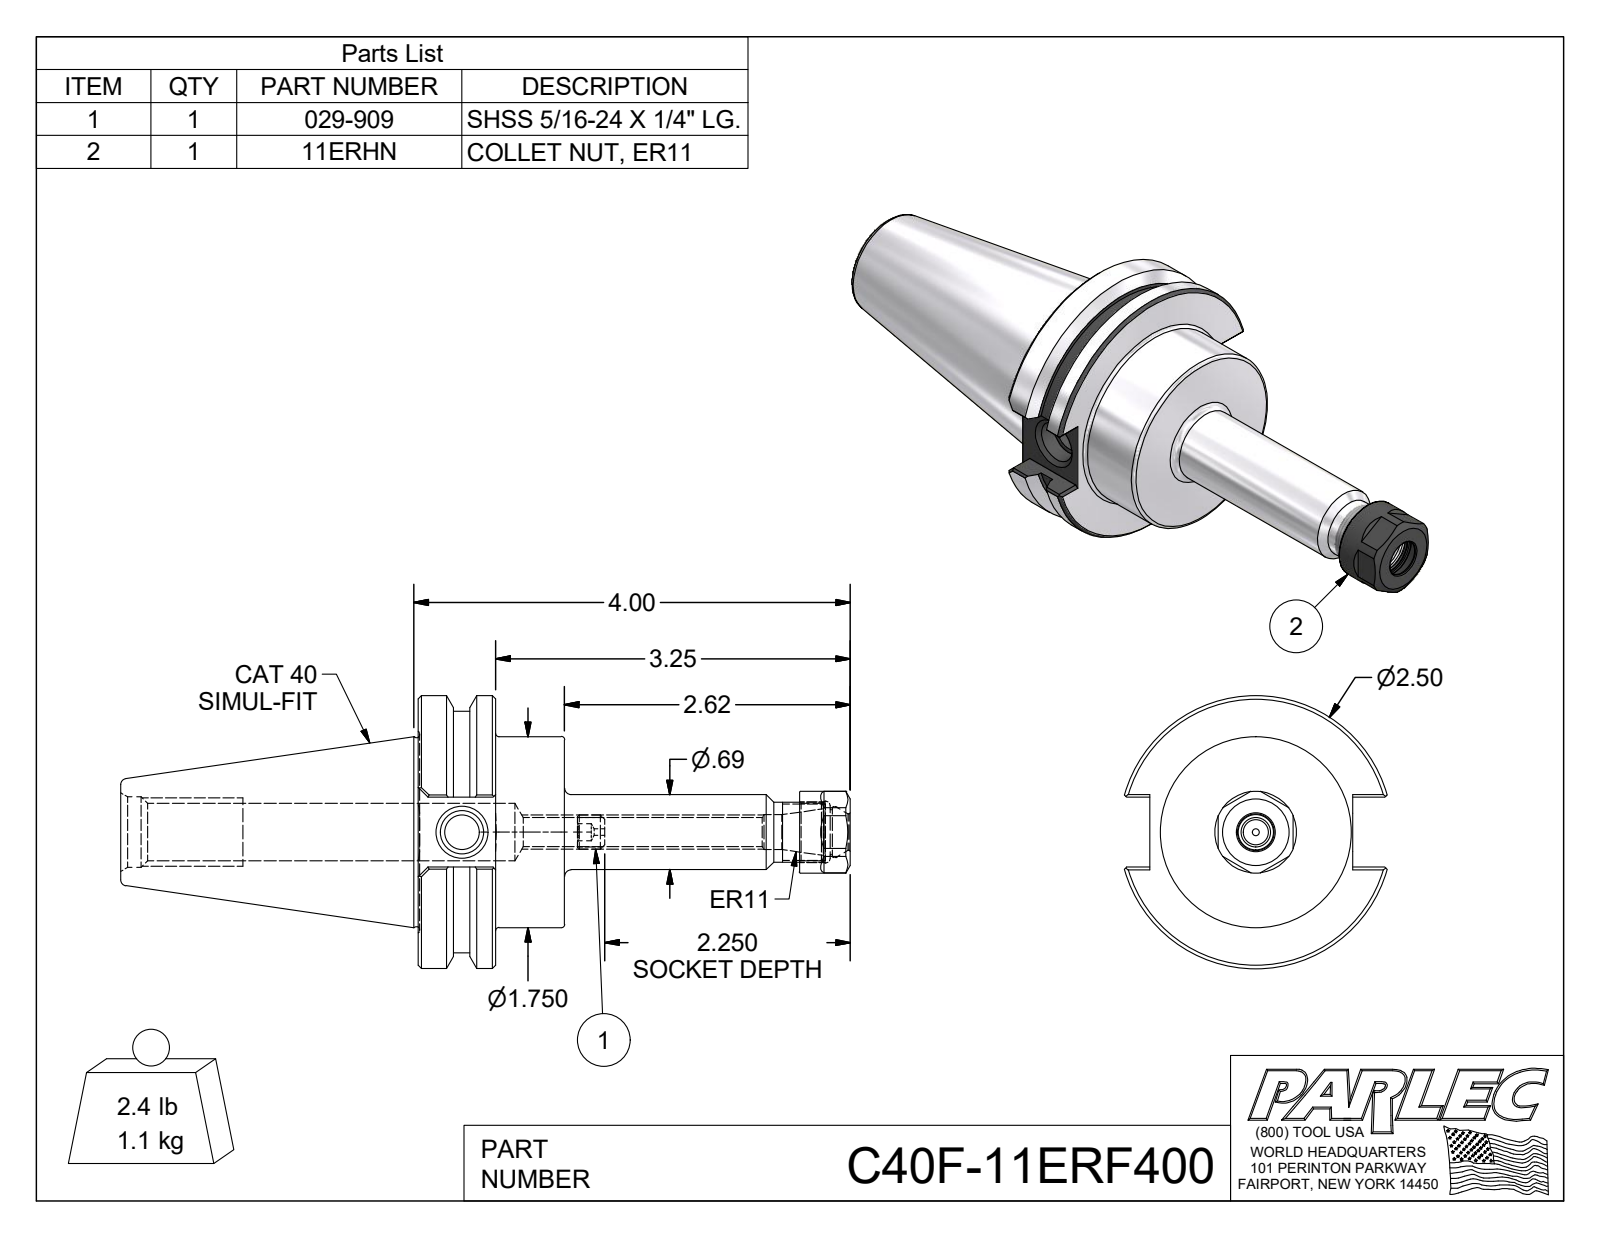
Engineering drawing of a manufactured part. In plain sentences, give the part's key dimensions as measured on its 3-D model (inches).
The part is named "C40F-11ERF400; 029-909; 11ERHN". Its 3-D file was written by "Autodesk Inventor 2016 (AUTOMOTIVE_DESIGN)". It is 3 solids with 133 faces: 62 planar, 22 cylindrical and 49 other. Overall it measures 6.687 by 2.5 by 2.406 inches. Its volume is 8.53 cubic inches and its surface area 45.71 square inches. Round holes: 1 of diameter 0.06, 1 of diameter 0.267, 1 of diameter 0.315, 1 of diameter 0.32, 1 of diameter 0.335, 1 of diameter 0.399, 1 of diameter 0.465, 1 of diameter 0.525, 1 of diameter 0.527, 1 of diameter 0.565, 1 of diameter 0.648. Round bosses or shafts: 1 of diameter 2.5, 1 of diameter 2.215, 1 of diameter 1.75, 1 of diameter 0.75, 1 of diameter 0.688, 1 of diameter 0.551, 1 of diameter 0.313. The main face-to-face distances are 0.63, 0.71, 1.34, 1.86, 0.64, 3.96, 3.25, 2.62, 2.727, 3.437.
